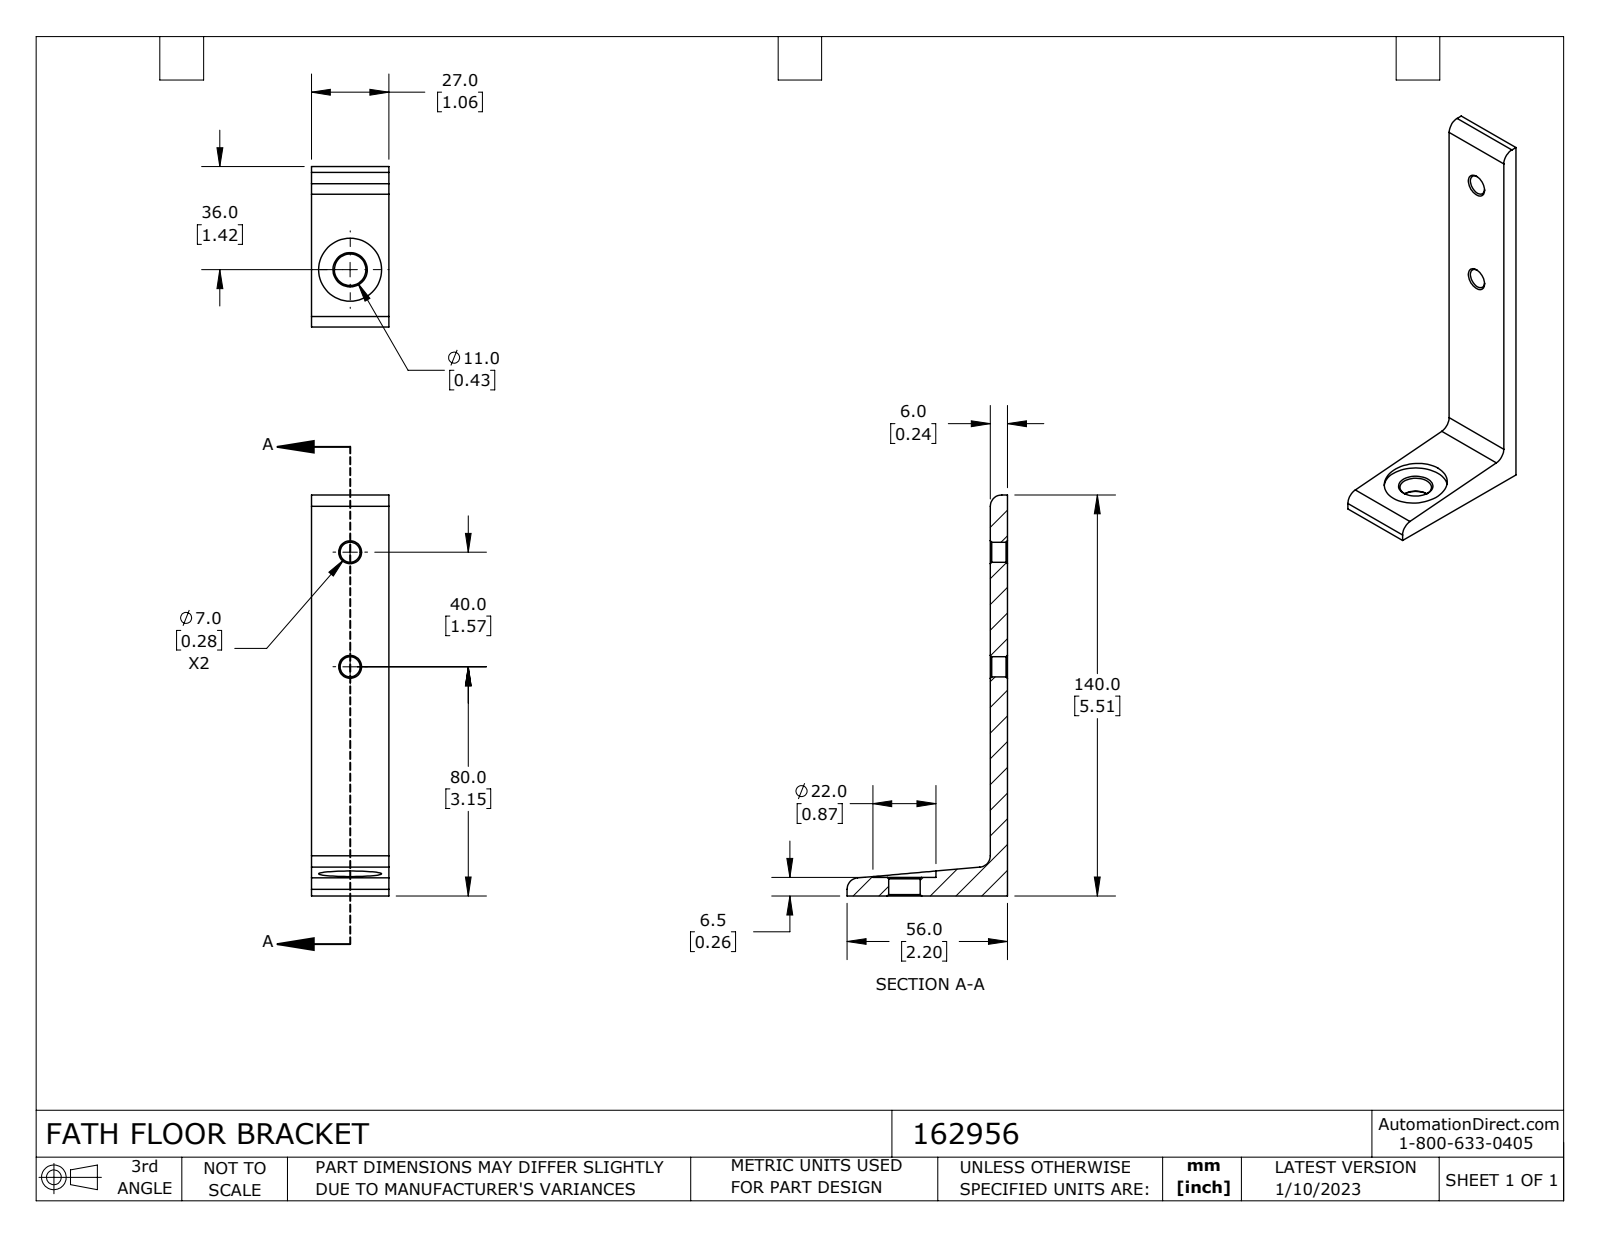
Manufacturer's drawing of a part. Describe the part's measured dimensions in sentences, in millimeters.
The part is named "162956". Its 3-D file was written by "SolidWorks 2021 (CONFIG_CONTROL_DESIGN)". It is 1 solid with 32 faces: 9 planar, 11 cylindrical and 12 other. Overall it measures 140 by 56 by 27 millimeters. Its volume is 32 070 cubic millimeters and its surface area 13 030 square millimeters. Round holes: 2 of diameter 7, 1 of diameter 11, 1 of diameter 22. Partial cylindrical surfaces (rounded edges, fillets, slot ends): 3 of radius 4. The main face-to-face distances are 6, 27, 6.5, 56, 50, 140, 133.5. The hole center spacings are 40.
